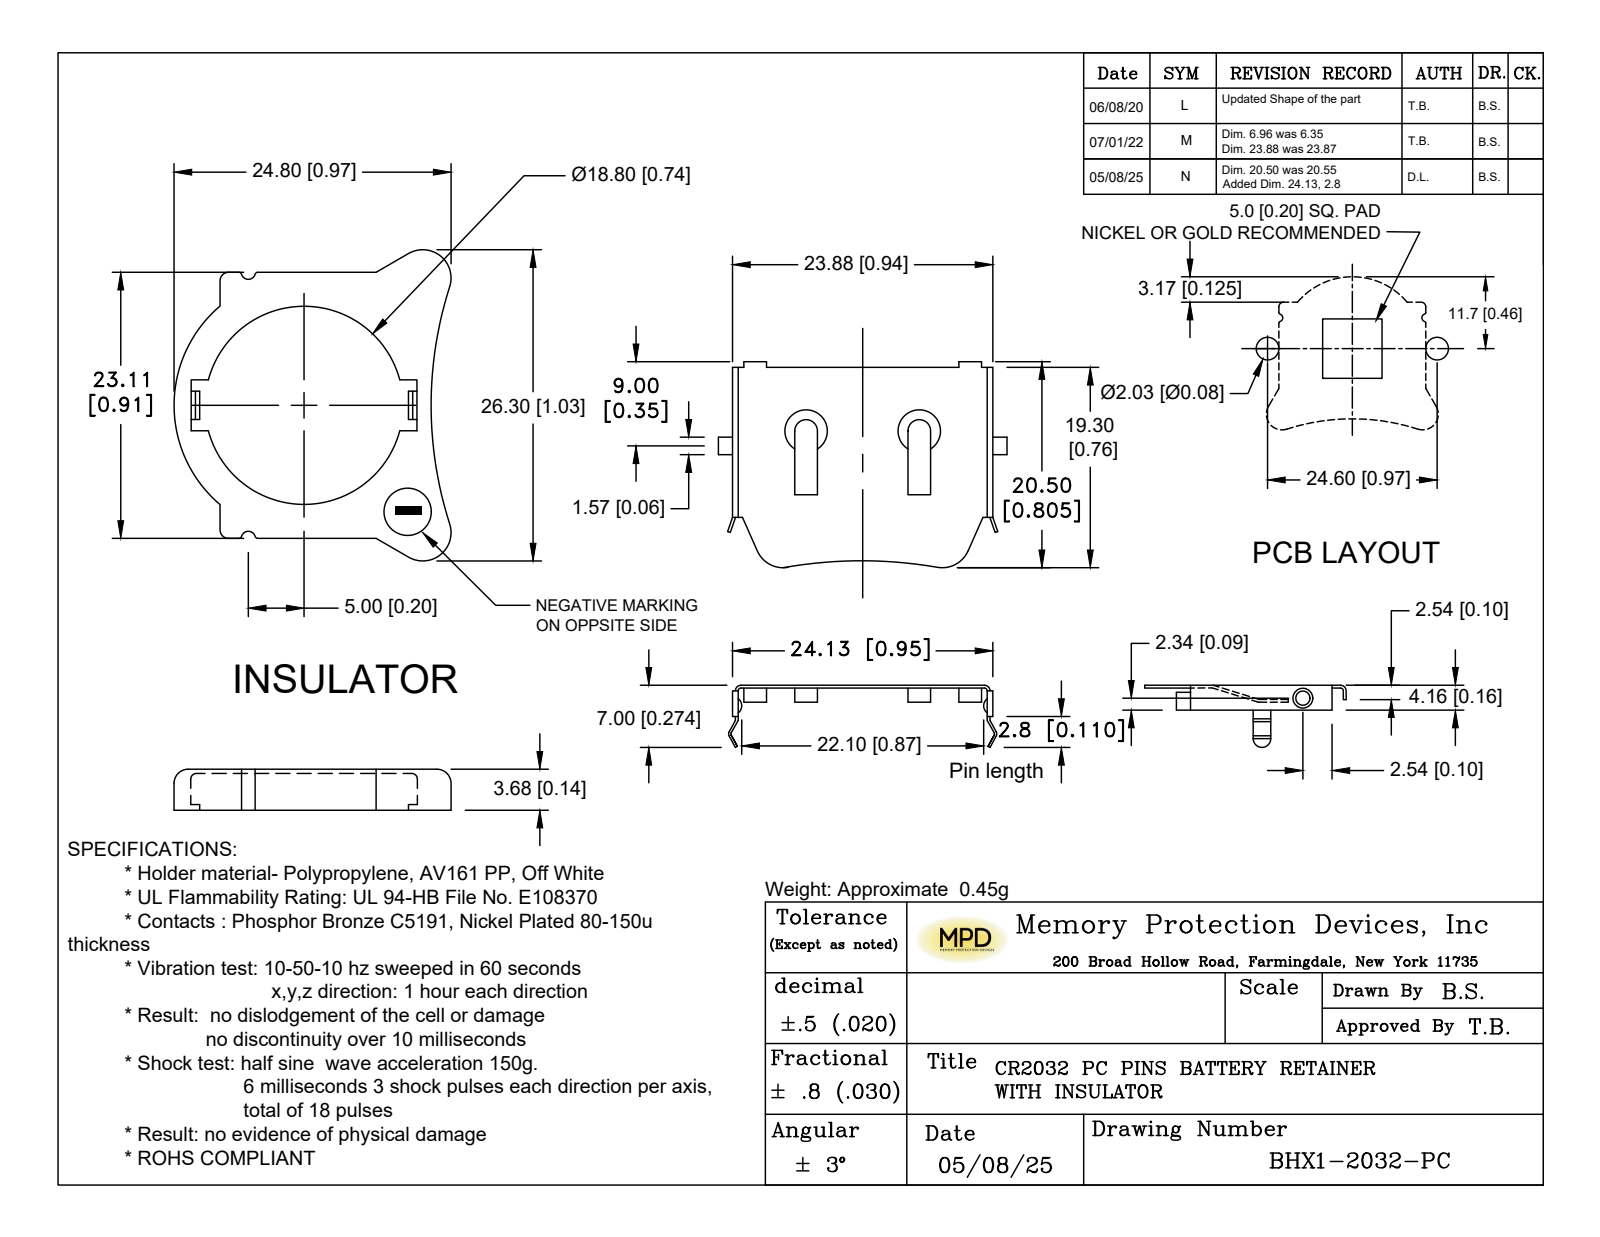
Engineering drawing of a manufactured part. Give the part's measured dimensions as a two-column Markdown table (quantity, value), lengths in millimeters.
| quantity | value |
| --- | --- |
| part name | BHX1-2032-PC |
| STEP written by | SolidWorks 2017 (AUTOMOTIVE_DESIGN) |
| units | millimeters |
| bodies | 2 solids, 285 faces (120 planar, 111 cylindrical, 54 other) |
| overall size | 26.3 × 24.8 × 6.35 |
| volume | 390 mm³ |
| surface area | 2 278 mm² |
| round holes (diameter × count) | 4 × 3, 1.54 × 1, 18.8 × 1 |
| round bosses / shafts (diameter × count) | 2 × 1 |
| partial cylindrical surfaces (radius × count) | 0.61 × 11, 0.1 × 7, 0.3 × 6, 0.15 × 4, 0.5 × 4, 0.81 × 4, 0.25 × 3, 0.48 × 3 |
| main face-to-face distances | 0.51, 3.42, 3.65, 3.93, 4.16, 23.65, 0.89, 22.99, 0.66, 22.76 |
| hole center spacings | 5.78, 10.16, 12.16, 12.47, 18.08 |
